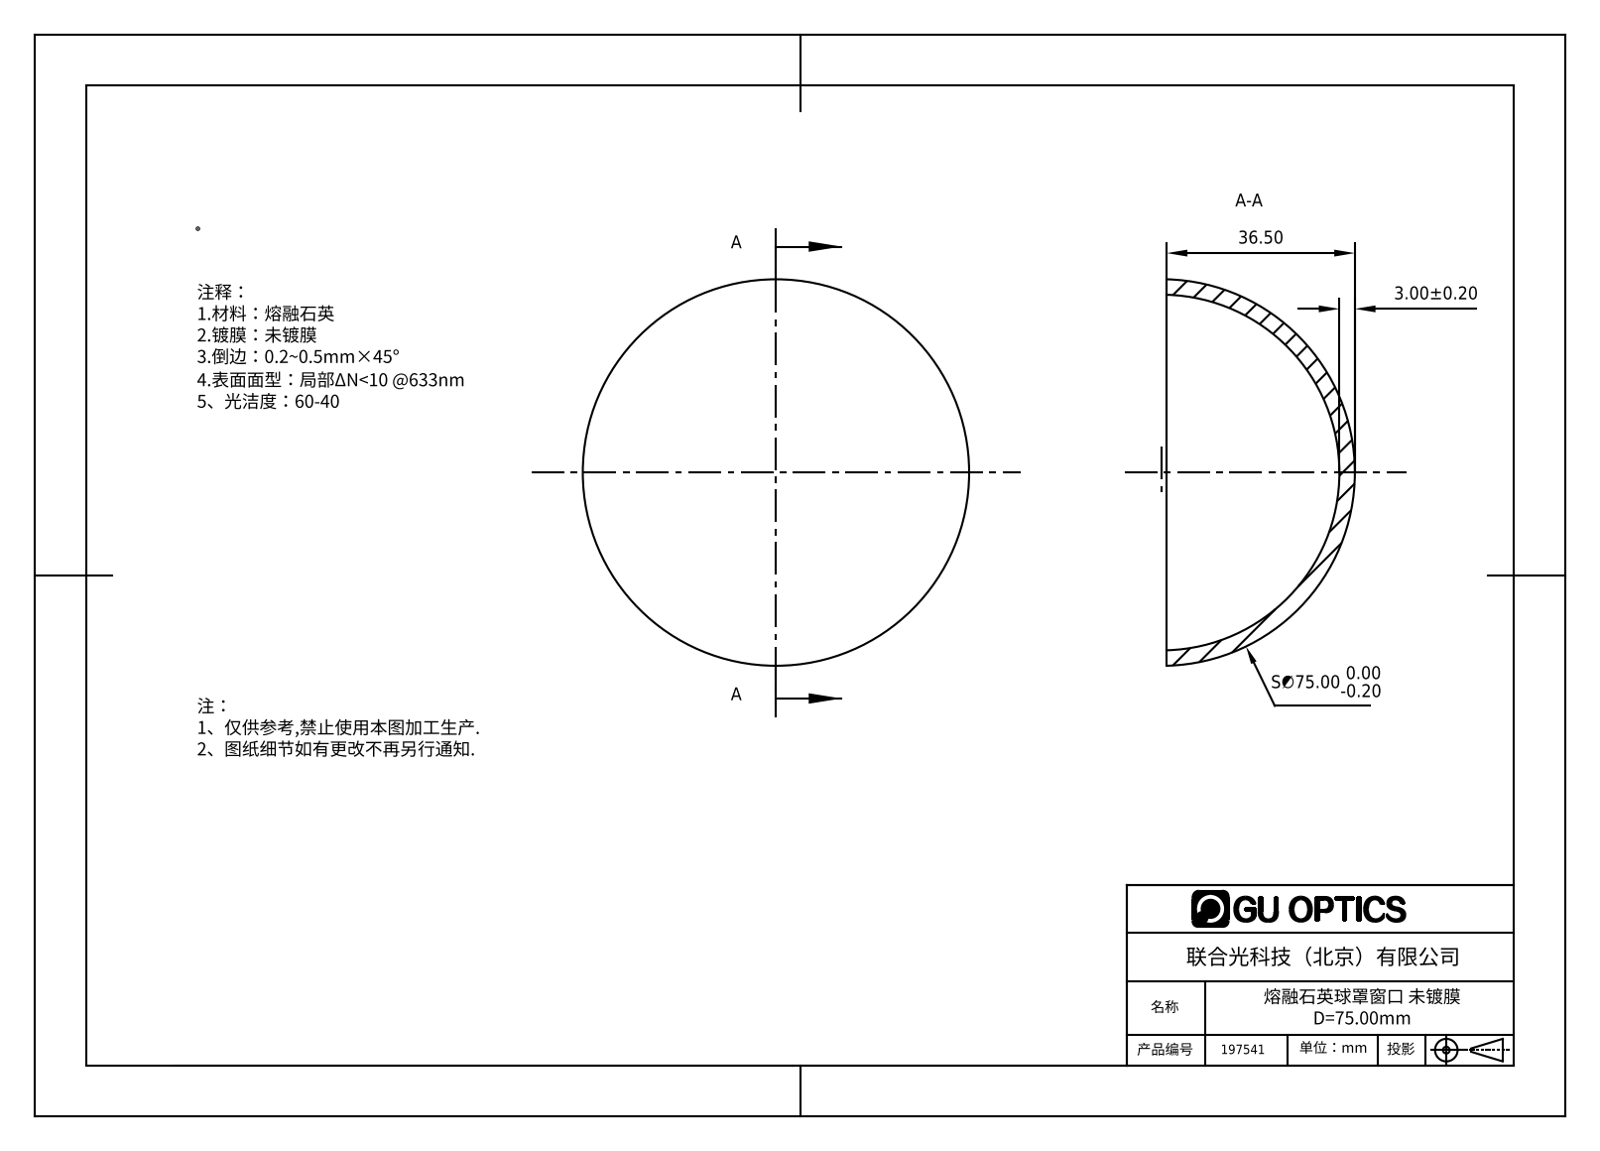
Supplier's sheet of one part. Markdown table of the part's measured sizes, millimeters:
| quantity | value |
| --- | --- |
| part name | 197537 |
| STEP written by | SolidWorks 2016 (AUTOMOTIVE_DESIGN) |
| units | millimeters |
| bodies | 1 solid, 5 faces (1 planar, 0 cylindrical, 4 other) |
| overall size | 74.97 × 74.97 × 36.5 |
| volume | 23 750 mm³ |
| surface area | 16 533 mm² |
